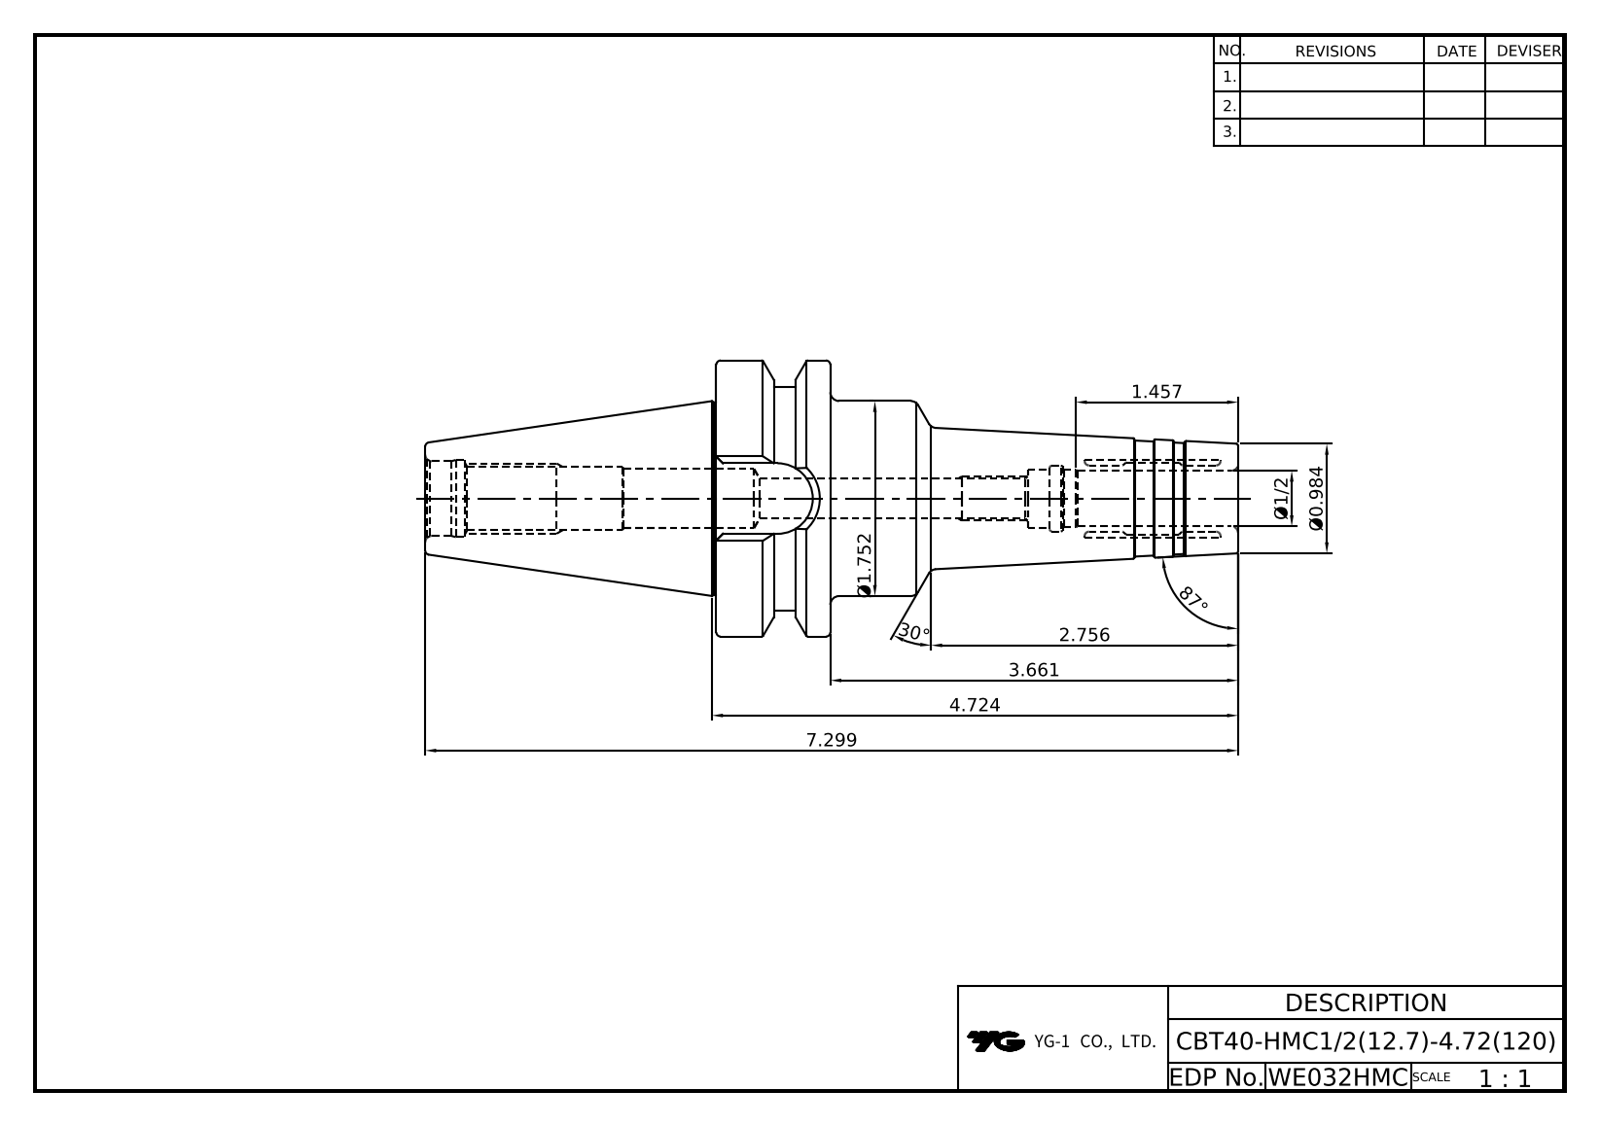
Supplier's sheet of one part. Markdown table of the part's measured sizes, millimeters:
| quantity | value |
| --- | --- |
| part name | LO-CBT40-HMC12.7-120 |
| STEP written by | Autodesk Inventor 2022 (AUTOMOTIVE_DESIGN) |
| units | millimeters |
| bodies | 1 solid, 81 faces (24 planar, 16 cylindrical, 41 other) |
| overall size | 185.4 × 63 × 63 |
| volume | 195 828 mm³ |
| surface area | 34 673 mm² |
| round holes (diameter × count) | 8.92 × 1, 12.7 × 1, 13.3 × 1, 13.5 × 1, 13.84 × 1, 17 × 1, 17.6 × 1 |
| round bosses / shafts (diameter × count) | 63 × 1, 51 × 1, 44.5 × 1, 44 × 1 |
| partial cylindrical surfaces (radius × count) | 8.05 × 1 |
| main face-to-face distances | 26, 119, 93, 45.2, 5, 18.1, 7.9, 100.9, 13.1, 12.9 |
